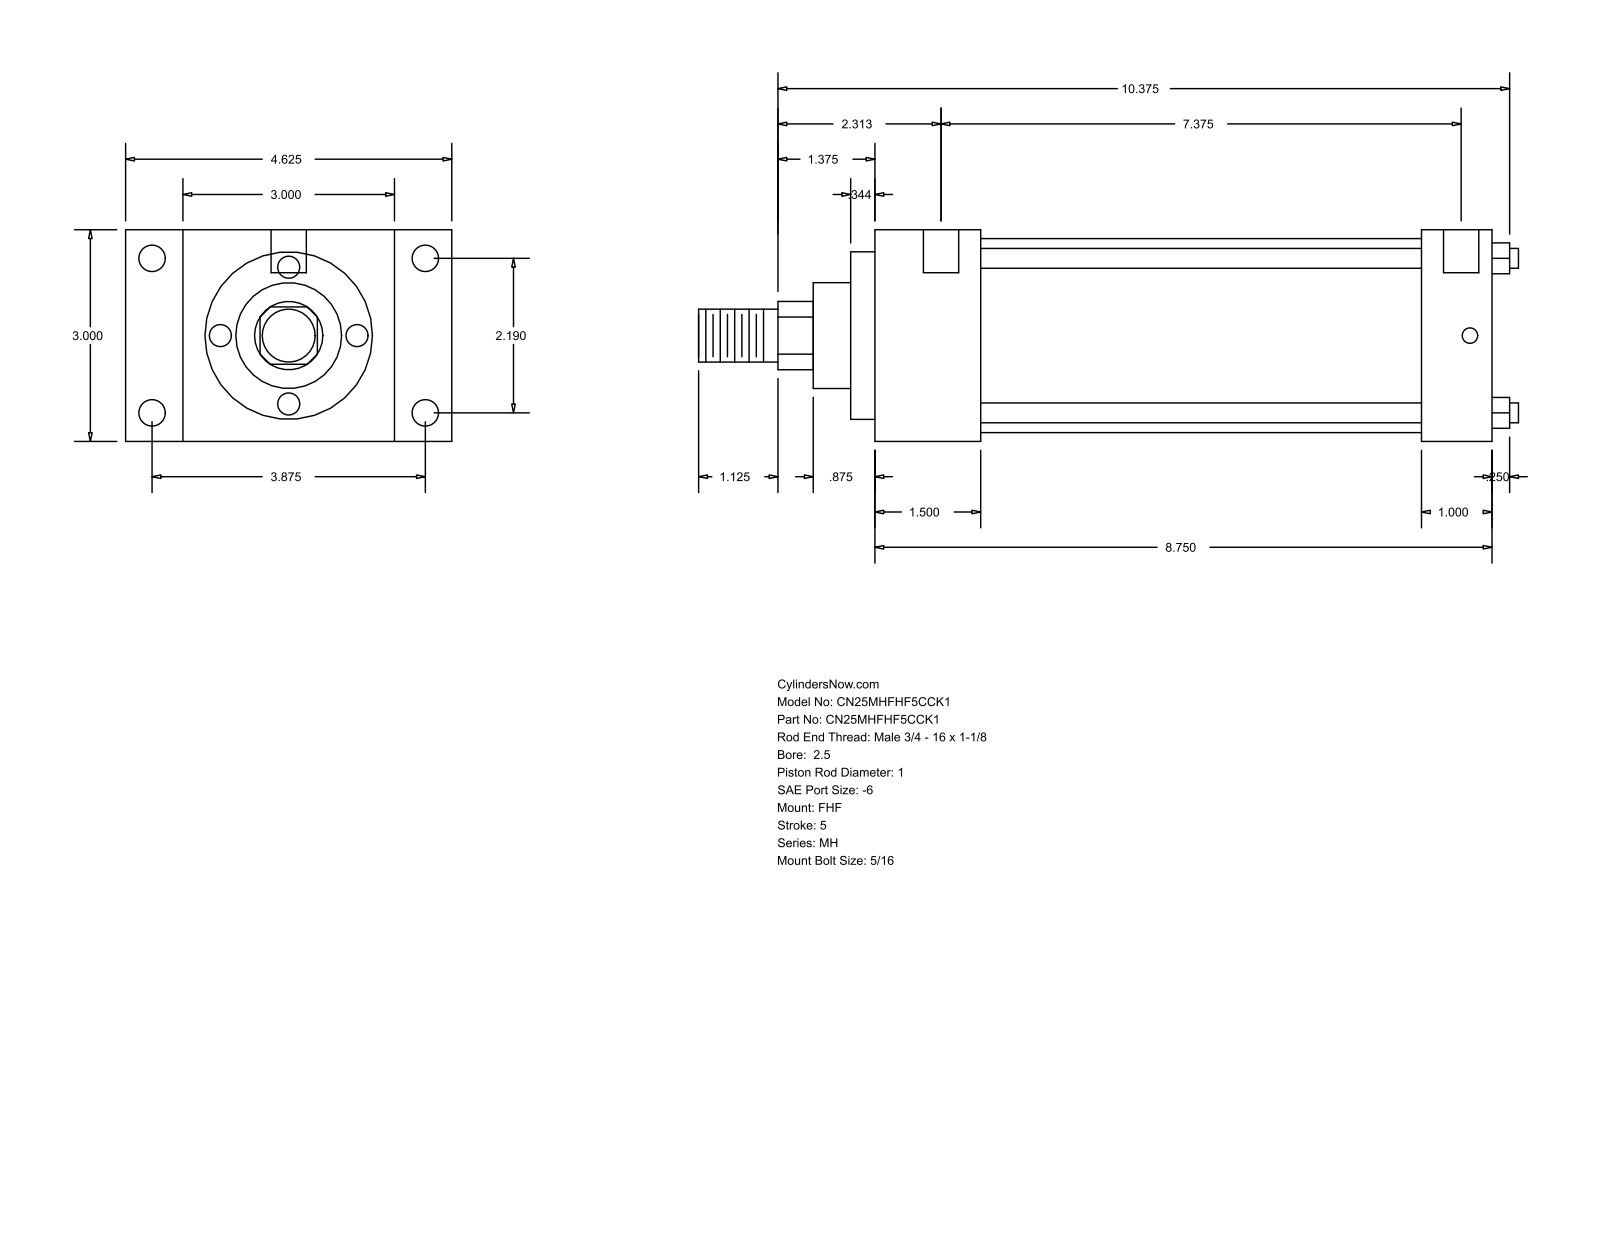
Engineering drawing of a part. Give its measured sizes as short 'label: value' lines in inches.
name: MH_FHF__0250_1
written by: GSSL Pune (CONFIG_CONTROL_DESIGN)
unit: in
bodies: 0 solids, 90 faces (61 planar, 29 cylindrical, 0 other)
size: 11.625 × 4.625 × 3
holes: 4× ⌀0.219, 4× ⌀0.375, 2× ⌀0.5
bosses: 4× ⌀0.281, 1× ⌀2.75, 1× ⌀2.375, 1× ⌀1.5, 1× ⌀1, 1× ⌀0.75
rounds: 1× R0.484
face distances: 3, 8.75, 1.5, 7.25, 0.813, 3.813, 4.625, 7.75, 6.25, 1
hole spacings: 2.19, 3.875, 4.451, 7.687, 0.125, 0.187, 7.375, 7.5
